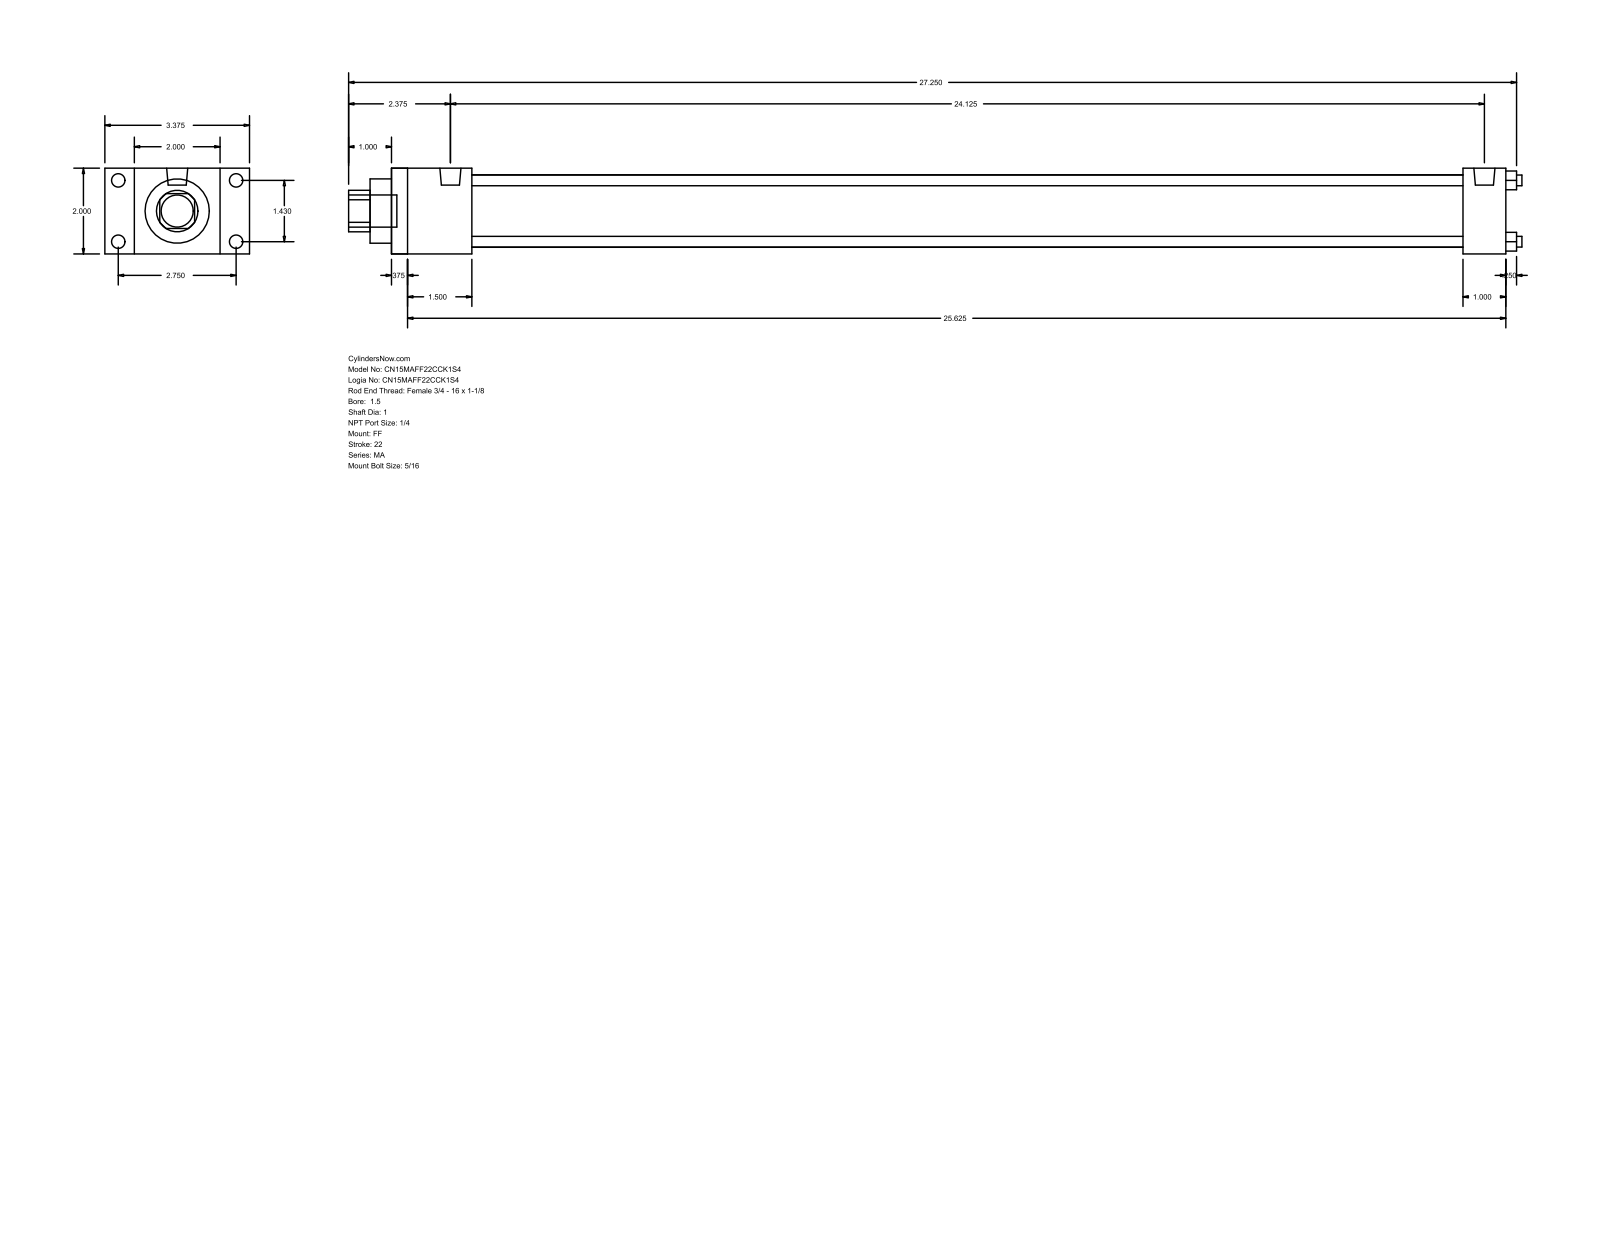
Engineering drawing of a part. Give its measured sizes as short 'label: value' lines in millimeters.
name: MA_FF__0150_1
written by: GSSL Pune (CONFIG_CONTROL_DESIGN)
unit: mm
bodies: 0 solids, 92 faces (64 planar, 28 cylindrical, 0 other)
size: 695.33 × 85.72 × 50.8
holes: 4× ⌀6.35, 1× ⌀25.4, 1× ⌀38.1, 1× ⌀42.93
bosses: 8× ⌀7.94, 2× ⌀12.49, 1× ⌀19.05
rounds: 1× R12.29
face distances: 50.8, 660.4, 9.52, 650.88, 25.4, 47.63, 635, 38.11, 625.48, 587.37
hole spacings: 25.68, 36.32, 51.36
